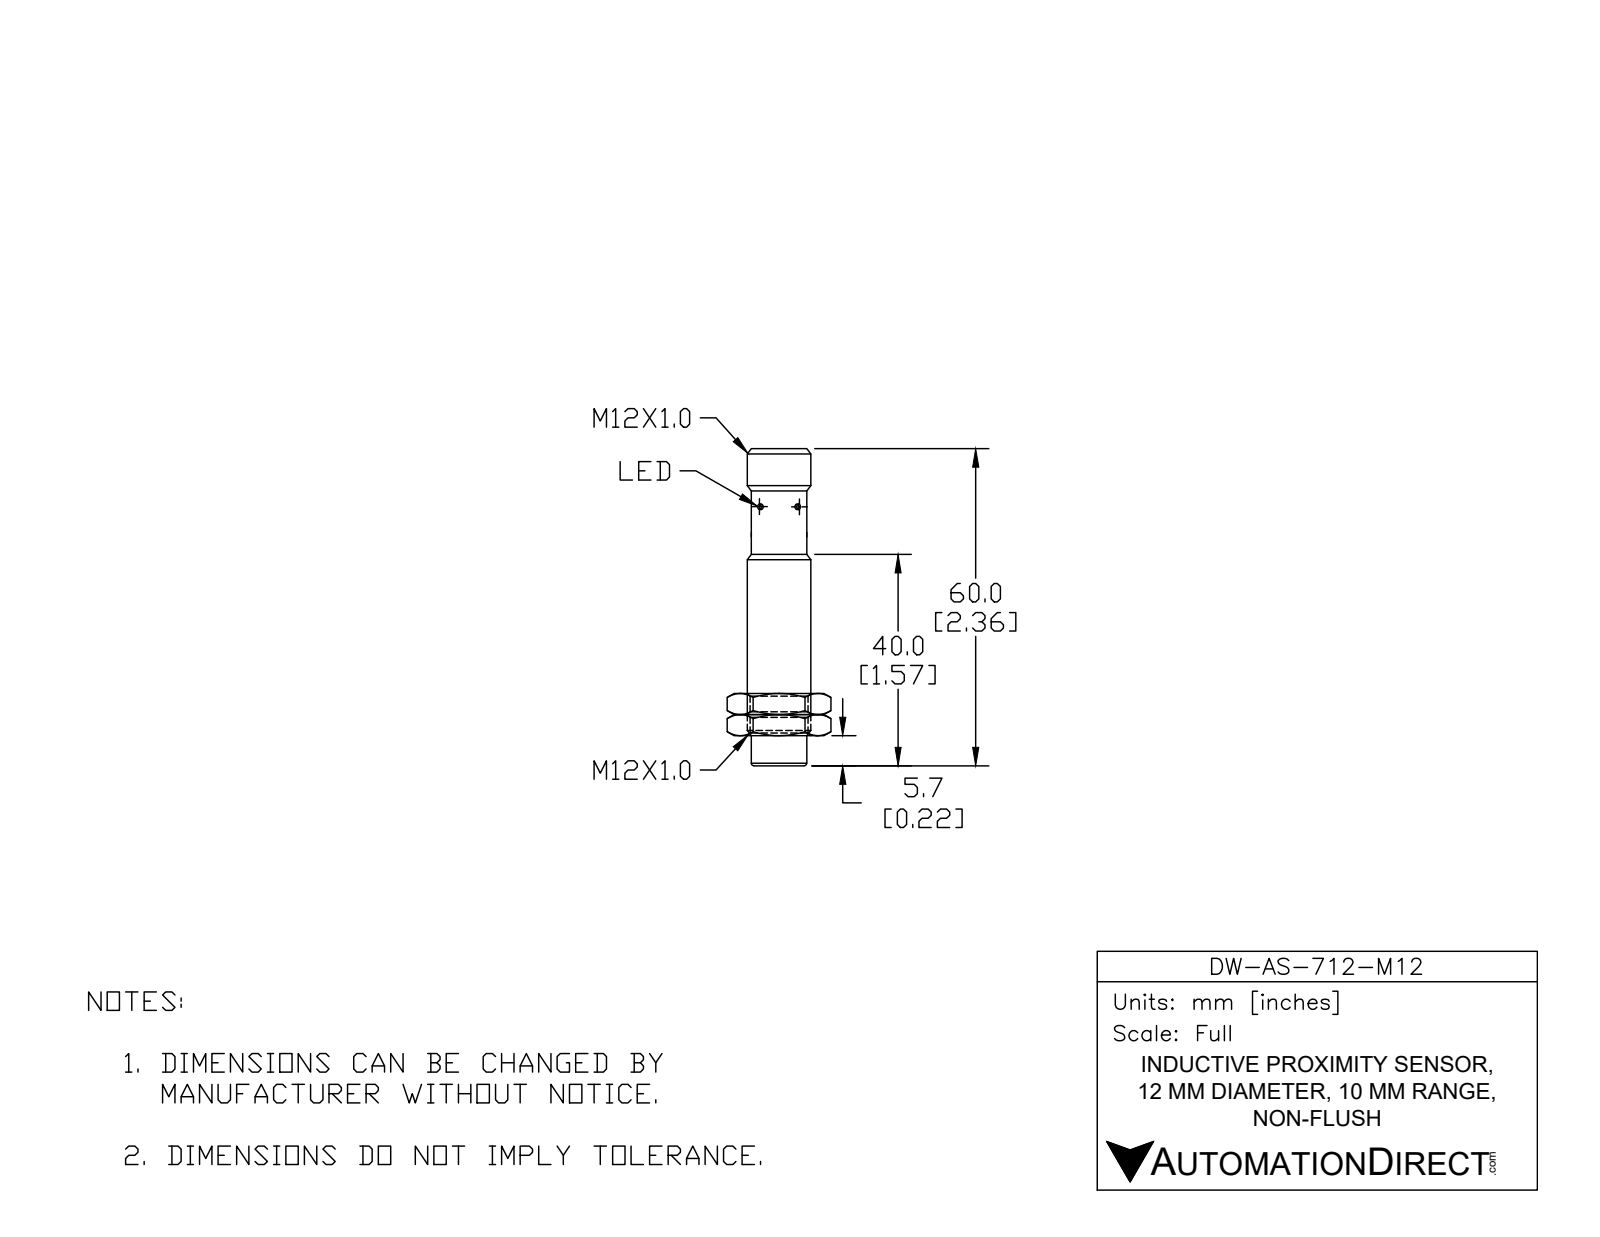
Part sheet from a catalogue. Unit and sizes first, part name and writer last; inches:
Units: inches
Overall size (bounding box): 2.362 × 0.472 × 0.472
Round holes (diameter × count): ⌀0.118 ×2, ⌀0.335 ×1
Round bosses / shafts (diameter × count): ⌀0.04 ×4, ⌀0.472 ×1, ⌀0.415 ×1
Partial cylindrical surfaces — rounded edges, fillets, slot ends (radius × count): R0.02 ×1, R0.02 ×1, R0.193 ×1
Main face-to-face distances: 2.02, 2.362, 0.343, 1.614, 0.406, 0.748, 2.047, 0.433, 0.028, 0.315
Volume: 0.359 in³ · Surface area: 4.295 in²
Bodies: 1 solid, 40 faces (9 planar, 20 cylindrical, 11 other)
Part name (STEP PRODUCT): DW-AS-712-M12
STEP written by: SolidWorks 2017 (AUTOMOTIVE_DESIGN)
